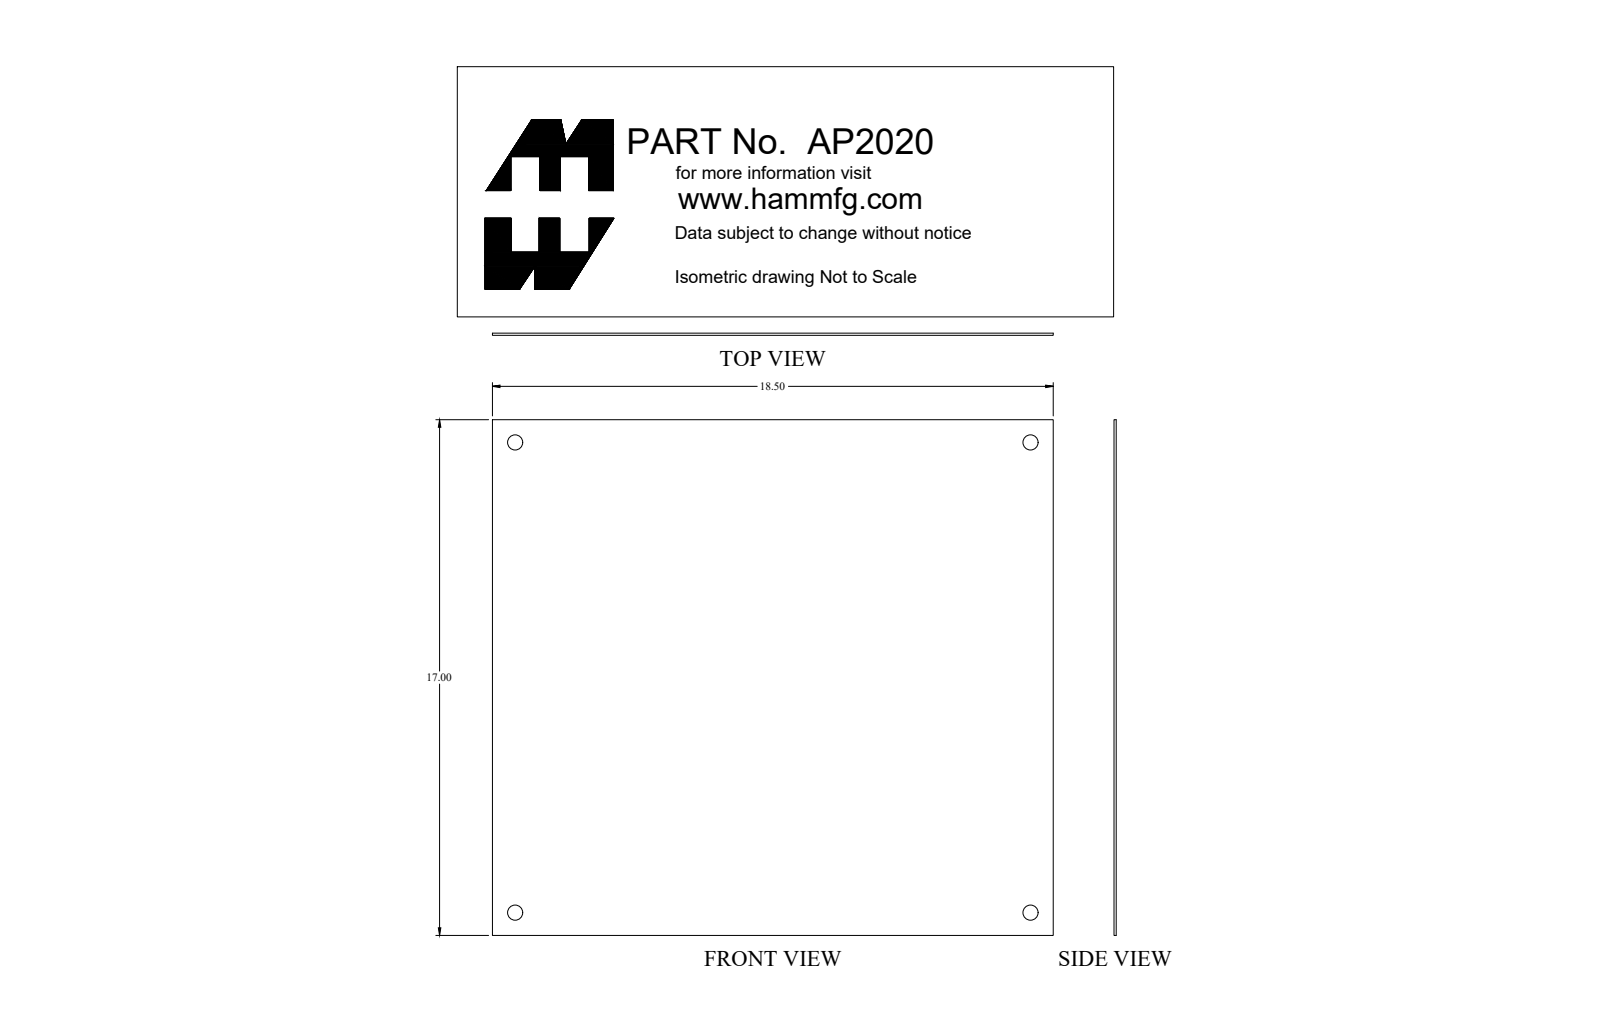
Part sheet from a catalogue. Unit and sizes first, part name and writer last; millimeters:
Units: millimetres
Overall size (bounding box): 469.9 × 431.8 × 1.8
Round holes (diameter × count): ⌀12.7 ×4
Main face-to-face distances: 1.8, 431.8, 469.9
Hole centre spacings: 393.7, 431.8, 584.4
Volume: 370 200 mm³ · Surface area: 408 400 mm²
Bodies: 1 solid, 14 faces (6 planar, 8 cylindrical, 0 other)
Part name (STEP PRODUCT): AP2020_Default
STEP written by: SolidWorks 2019 (CONFIG_CONTROL_DESIGN)
